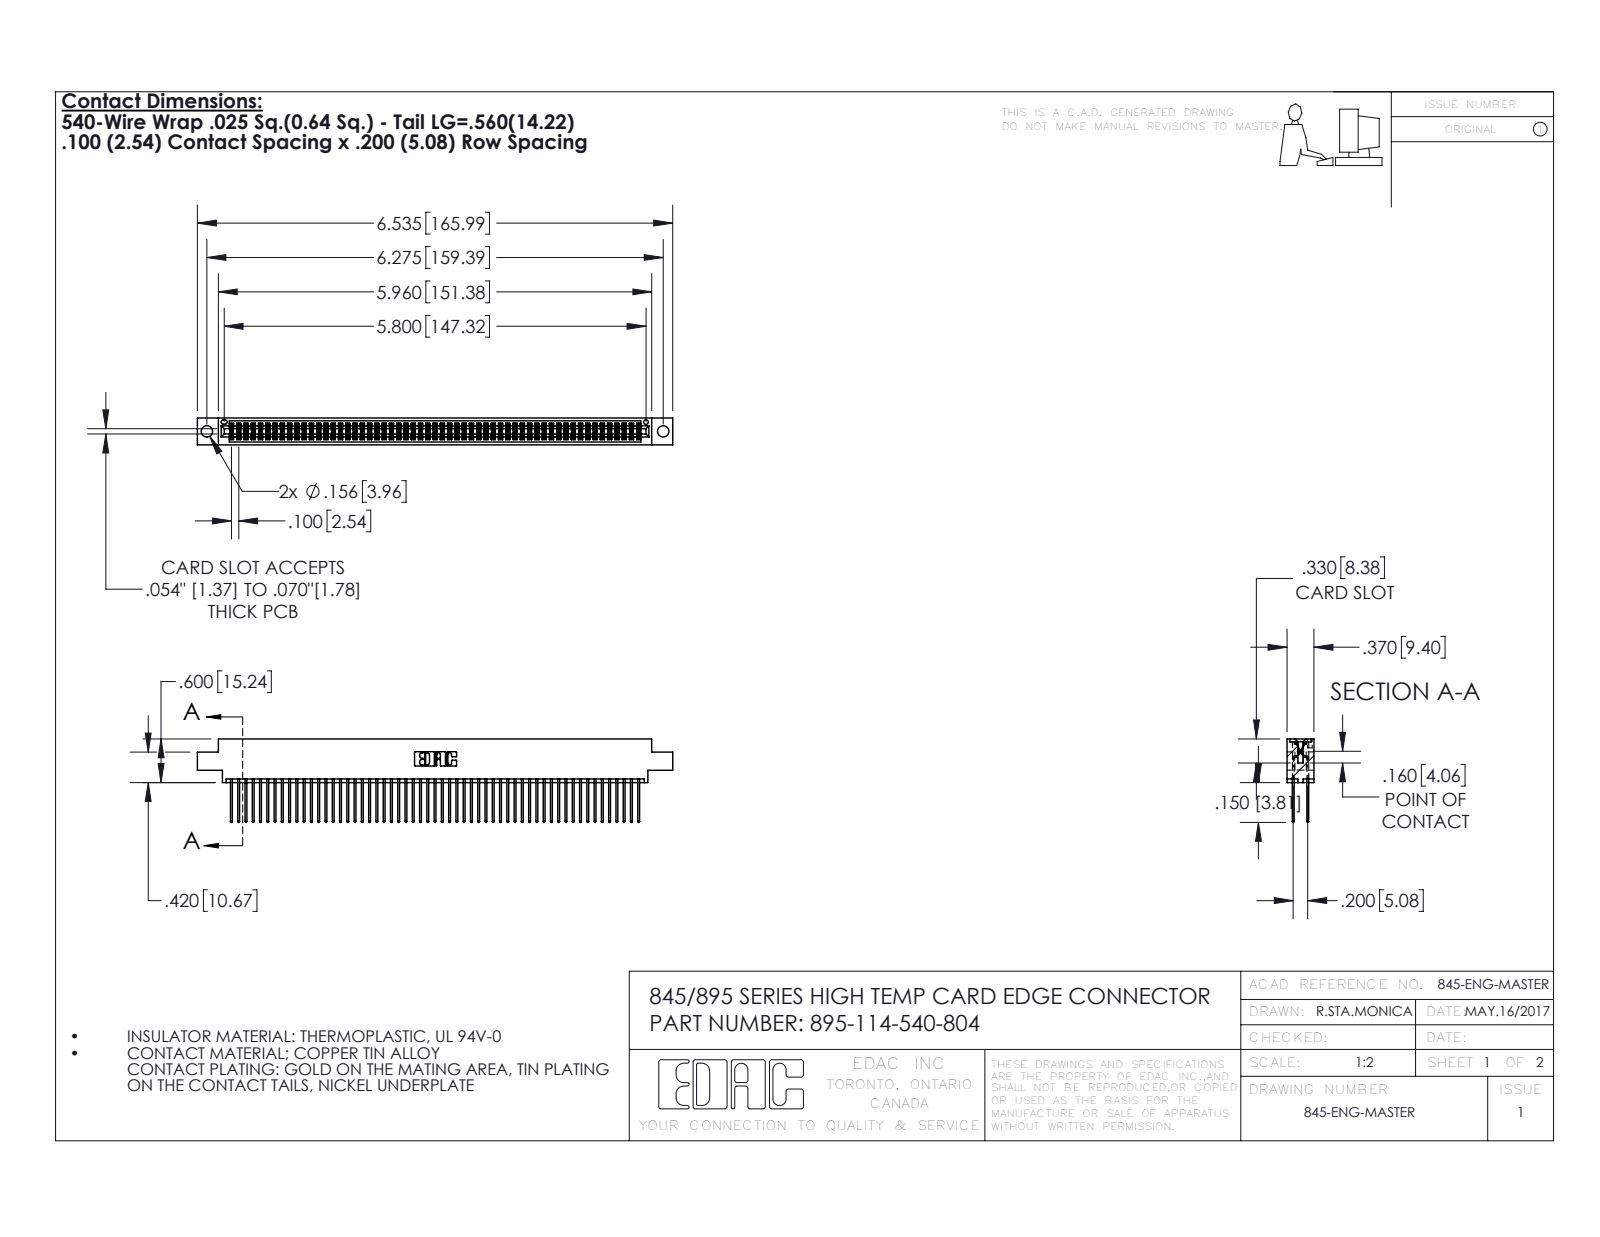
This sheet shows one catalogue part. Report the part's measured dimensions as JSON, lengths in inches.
{"part_name": "395-114-540-804; 345-292-001_345-293-140; 345 Part_0.170 Offset - 0.156 Dia-TH", "step_written_by": "SolidWorks 2016 (CONFIG_CONTROL_DESIGN)", "units": "inches", "bodies": {"solids": 115, "faces": 5830, "planar": 3846, "cylindrical": 1984, "other": 0}, "overall_size": [6.535, 1.147, 0.37], "volume_in3": 1.007, "surface_area_in2": 41.29, "round_holes": [[0.156, 2], [0.064, 1]], "partial_cylinders_radius": [[0.006, 171], [0.01, 114], [0.01, 22], [0.007, 6], [0.031, 6], [0.026, 3], [0.014, 2], [0.019, 2]], "face_to_face_distances": [0.072, 0.298, 0.2, 0.098, 0.272, 0.025, 0.37, 0.225, 0.175, 0.149], "hole_center_spacings": [0.27, 6.039, 6.275]}
